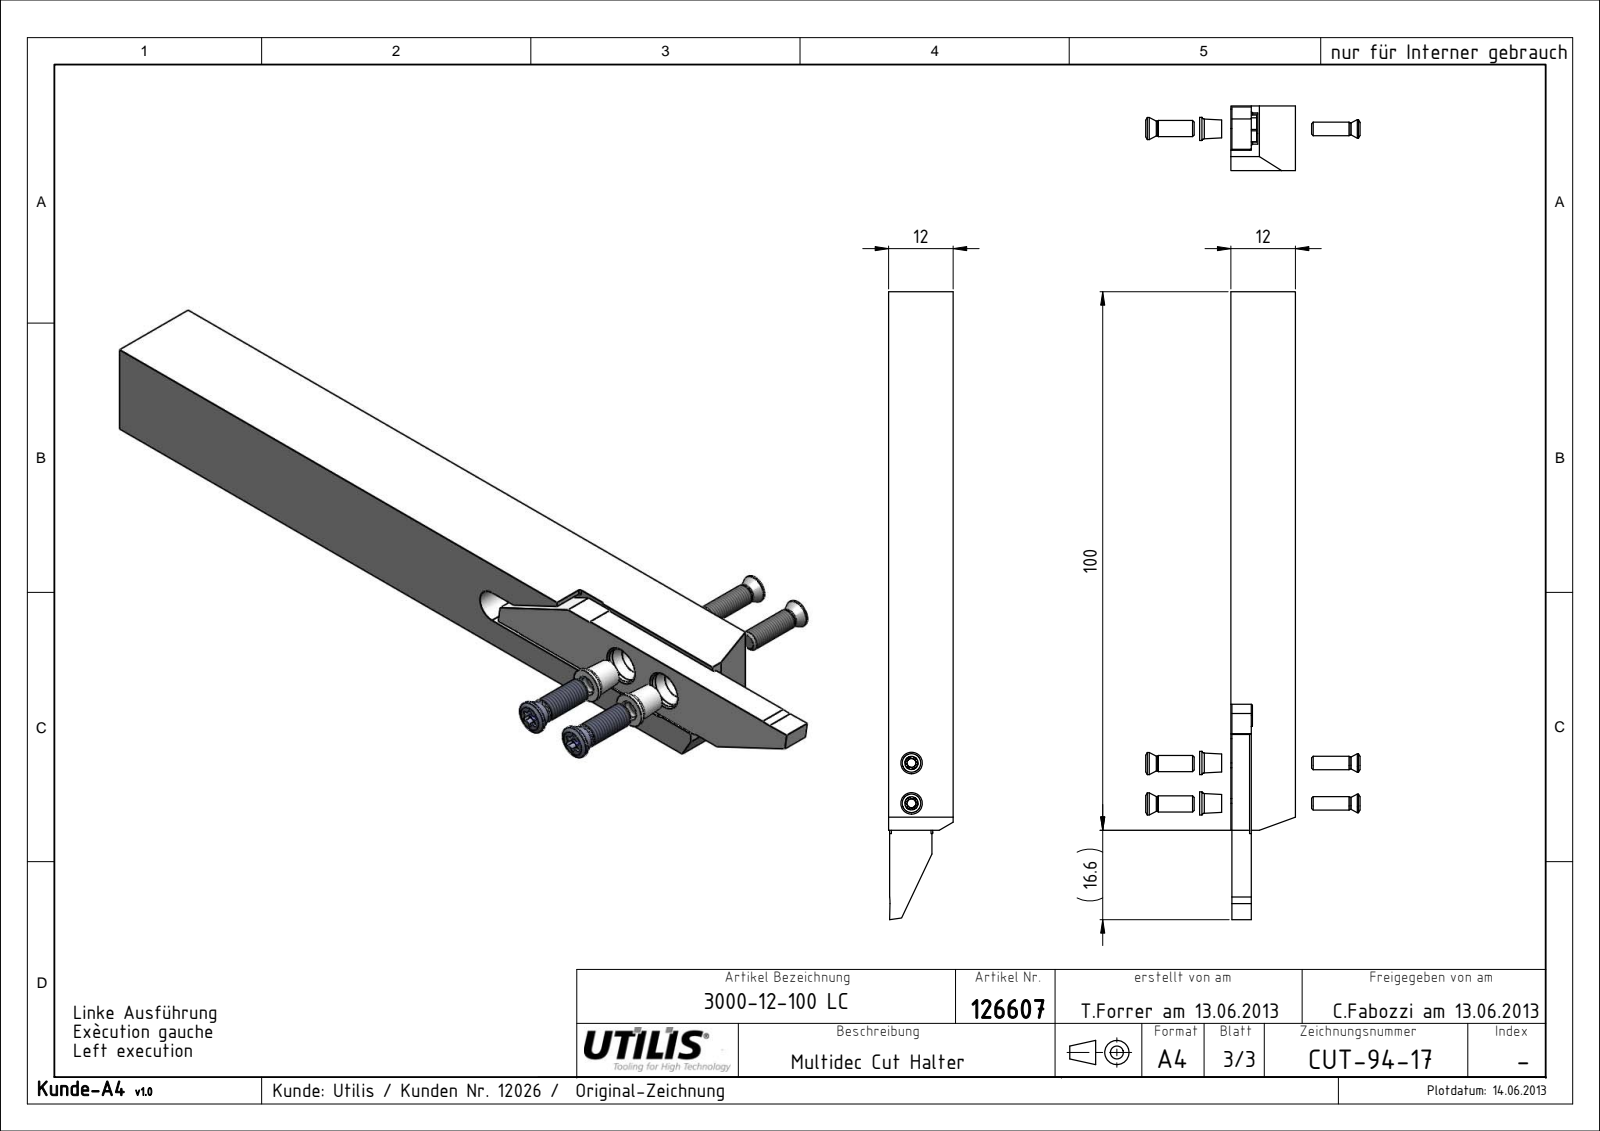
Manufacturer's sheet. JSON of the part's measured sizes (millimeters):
{"part_name": "MSP-16_M3x7.3 T08; CUT-3000 R-L Kunde Lang_Lang; CUT-93-Kunde_3000-12-100 L; CUT-93-18", "step_written_by": "SolidWorks 2013 (CONFIG_CONTROL_DESIGN)", "units": "millimeters", "bodies": {"solids": 4, "faces": 137, "planar": 42, "cylindrical": 55, "other": 40}, "overall_size": [116.5, 12, 12], "volume_mm3": 14412, "surface_area_mm2": 6499, "round_holes": [[2.5, 2], [3.55, 2]], "round_bosses_or_shafts": [[4.1, 2], [3, 2]], "partial_cylinders_radius": [[0.2, 12], [0.45, 12], [2.1, 4], [0.15, 2], [10, 2]], "face_to_face_distances": [12, 3.8, 8.2, 3.6, 11.8, 11.88, 3.88, 8, 8.12, 3.55], "hole_center_spacings": [7.5]}
